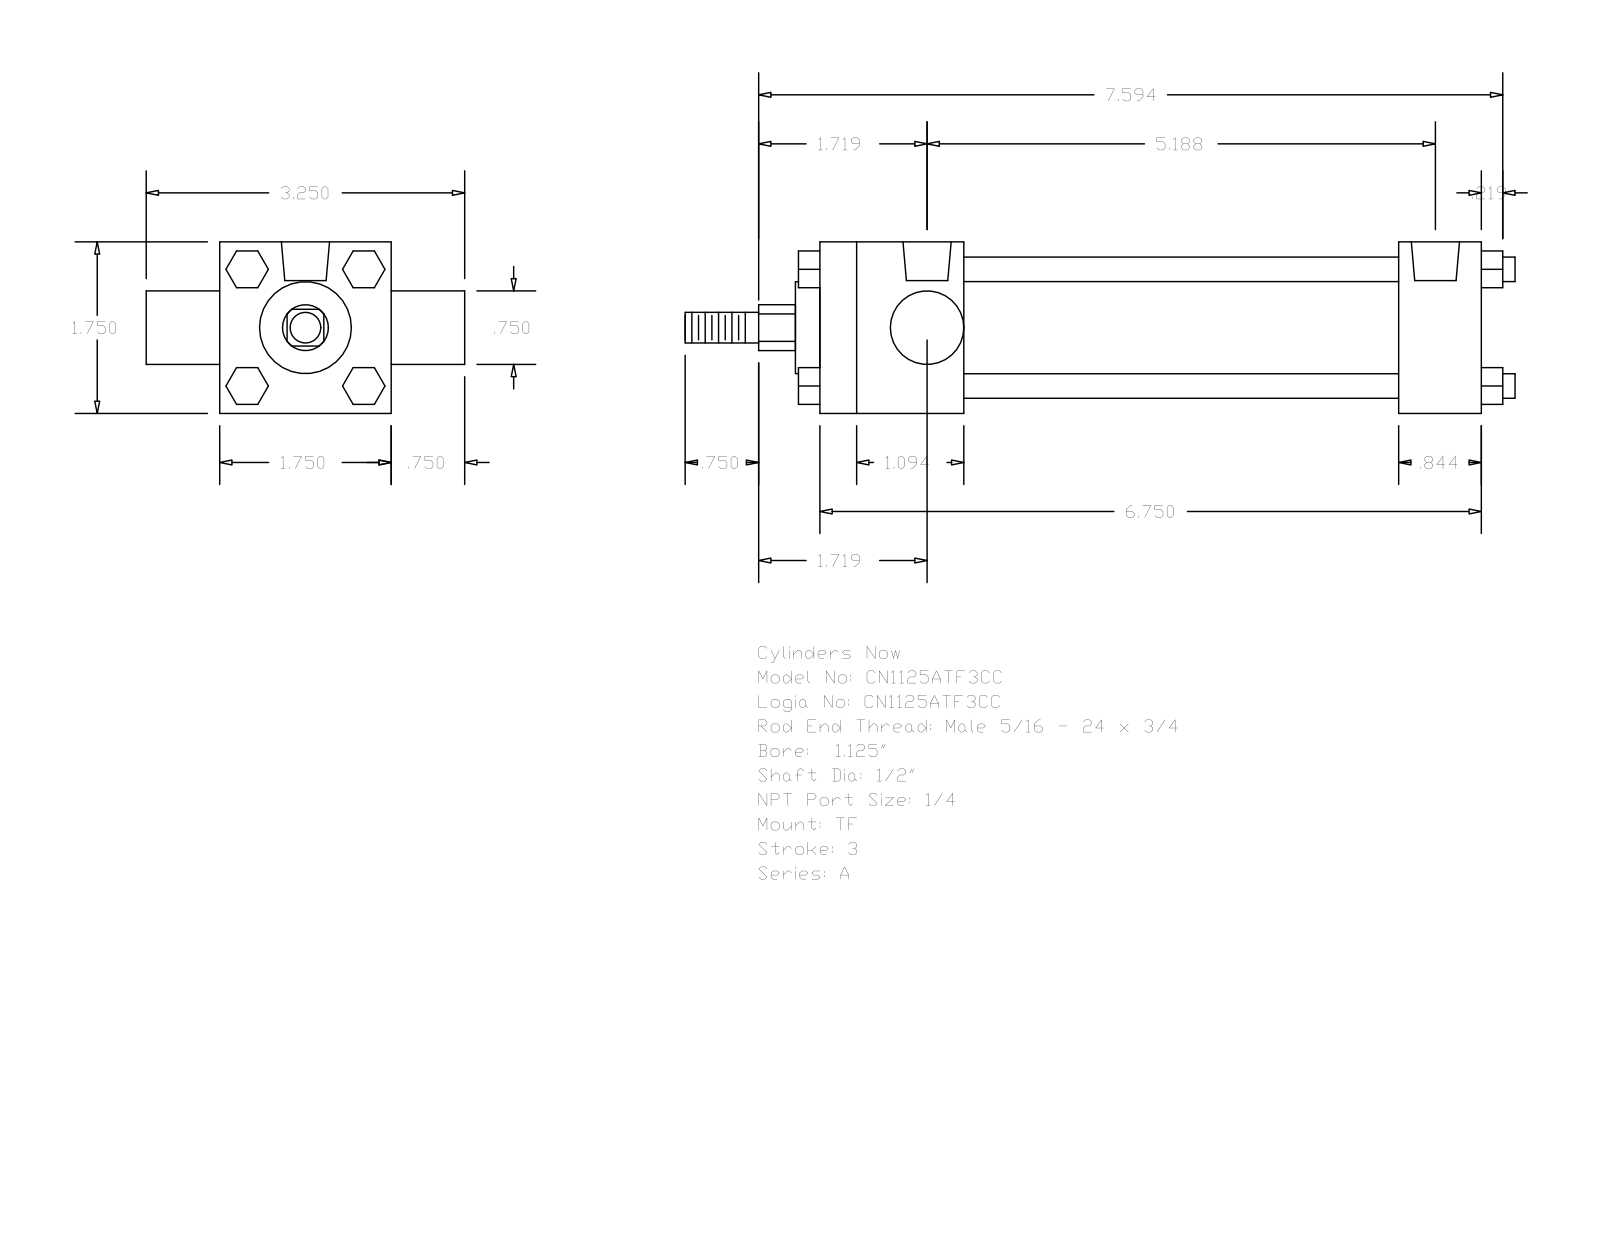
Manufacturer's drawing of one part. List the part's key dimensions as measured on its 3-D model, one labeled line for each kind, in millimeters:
Part name (STEP PRODUCT): A_TF__0112_0.5
STEP written by: GSSL Pune (CONFIG_CONTROL_DESIGN)
Units: millimetres
Bodies: 0 solids, 120 faces (92 planar, 28 cylindrical, 0 other)
Overall size (bounding box): 215.11 × 82.55 × 44.45
Round holes (diameter × count): ⌀5.56 ×3, ⌀12.49 ×2
Round bosses / shafts (diameter × count): ⌀6.35 ×4, ⌀31.88 ×1, ⌀23.81 ×1, ⌀19.05 ×1, ⌀12.7 ×1, ⌀7.94 ×1
Partial cylindrical surfaces — rounded edges, fillets, slot ends (radius × count): R5.94 ×1
Main face-to-face distances: 44.46, 171.44, 150.01, 21.43, 37.3, 112.71, 134.14, 19.04, 63.5, 9.53
Hole centre spacings: 1.58, 1.59, 128.59, 130.17, 130.18, 131.76
